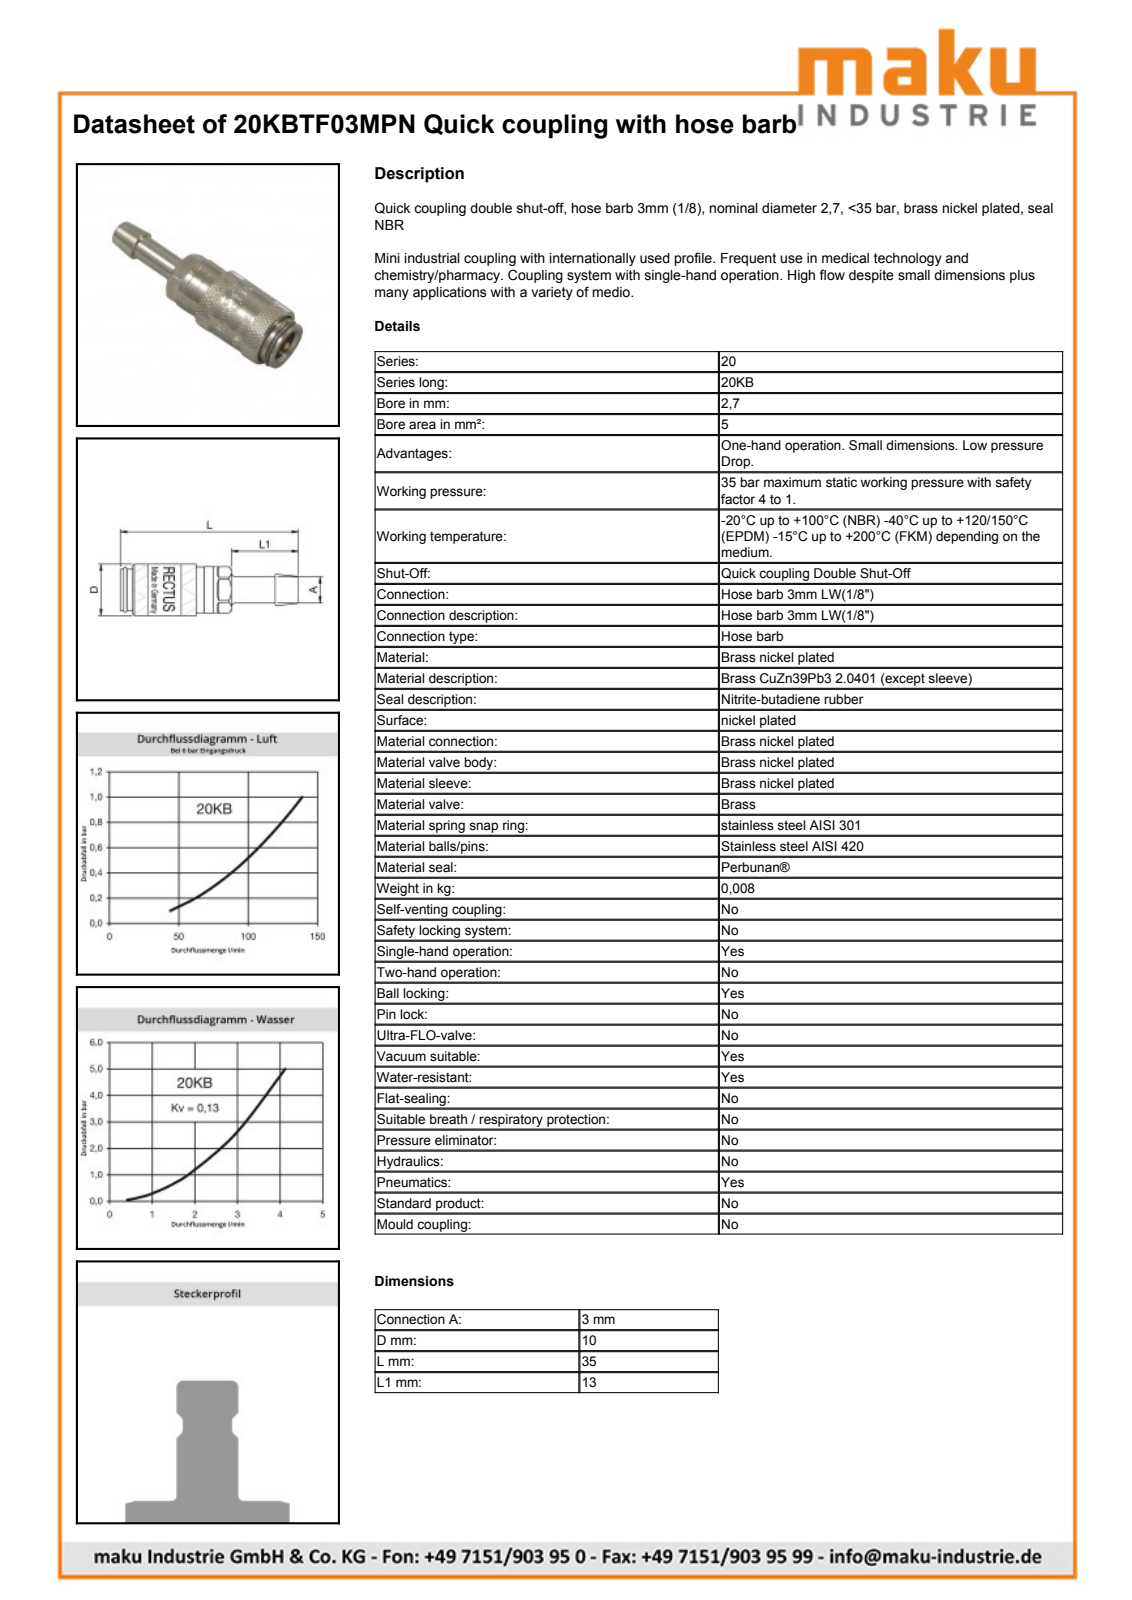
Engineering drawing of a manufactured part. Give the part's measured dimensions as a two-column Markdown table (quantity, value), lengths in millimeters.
| quantity | value |
| --- | --- |
| part name | D104279 |
| STEP written by | Autodesk Inventor 2013 (AUTOMOTIVE_DESIGN) |
| units | millimeters |
| bodies | 2 solids, 441 faces (170 planar, 59 cylindrical, 212 other) |
| overall size | 34.55 × 10.35 × 10.35 |
| volume | 1 501 mm³ |
| surface area | 1 873 mm² |
| round holes (diameter × count) | 7.46 × 1, 8.1 × 1, 8.15 × 1, 9.15 × 1, 9.2 × 1 |
| round bosses / shafts (diameter × count) | 10.35 × 1, 10 × 1, 9.8 × 1, 9 × 1, 8.9 × 1, 8 × 1, 7.8 × 1, 7.4 × 1 |
| partial cylindrical surfaces (radius × count) | 3.38 × 1 |
| main face-to-face distances | 21.55, 8, 3.2, 2.5, 19.05, 5, 18, 15.5, 3.55, 14.8 |
